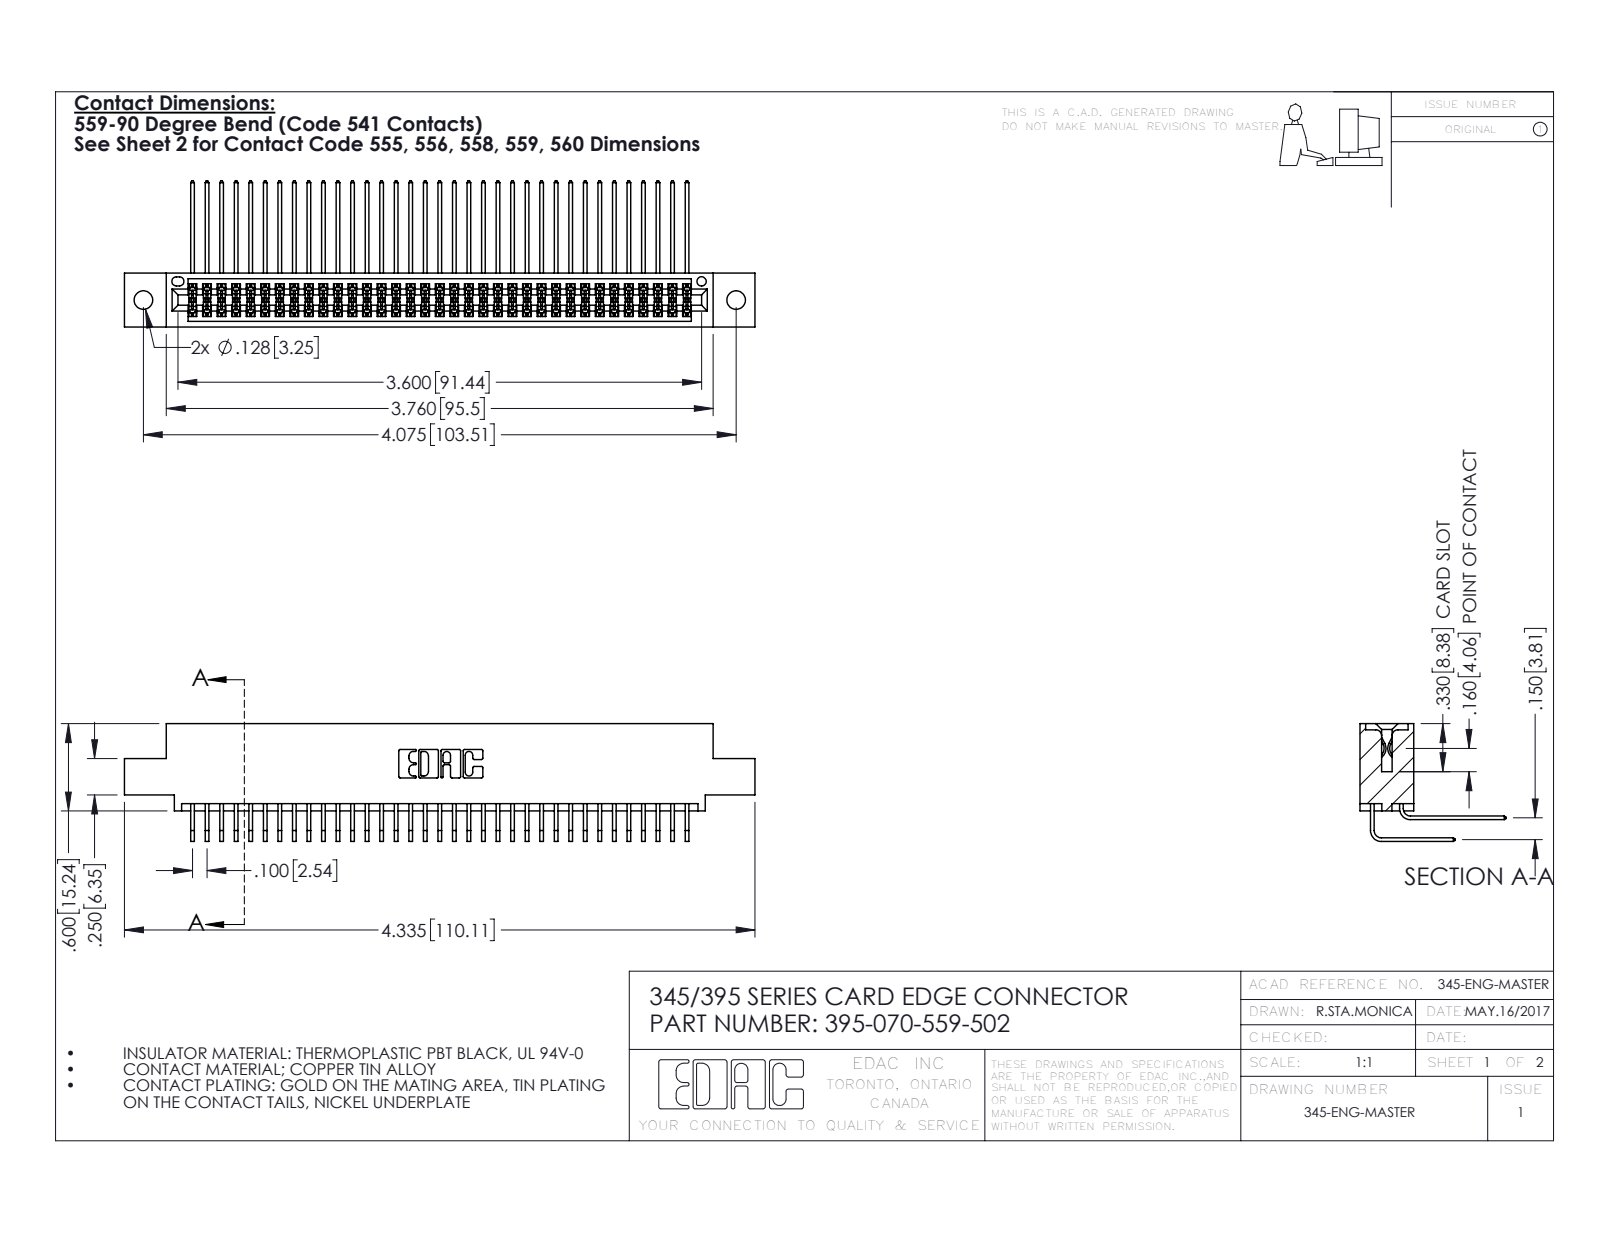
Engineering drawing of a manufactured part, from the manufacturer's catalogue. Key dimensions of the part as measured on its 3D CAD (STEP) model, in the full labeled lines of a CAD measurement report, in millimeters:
Part name (STEP PRODUCT): 345-292-001_558 559 Tail - 1; 345-292-001_559 Tail - 2; 345 Part_0.110 Offset - 0.128 Dia; 395-070-559-502
STEP written by: SolidWorks 2016 (CONFIG_CONTROL_DESIGN)
Units: millimetres
Bodies: 71 solids, 3770 faces (2534 planar, 1236 cylindrical, 0 other)
Overall size (bounding box): 110.1 × 25.5 × 20.5
Volume: 10 900 mm³ · Surface area: 17 730 mm²
Round holes (diameter × count): ⌀3.3 ×2, ⌀1.6 ×1
Partial cylindrical surfaces — rounded edges, fillets, slot ends (radius × count): R0.2 ×105, R0.3 ×22, R0.2 ×6, R0.8 ×6, R0.7 ×3, R0.4 ×2, R0.5 ×2, R0.6 ×2
Main face-to-face distances: 1.8, 7.6, 9.4, 5.1, 2.5, 6.9, 0.6, 5.7, 4.4, 3.8
Hole centre spacings: 6.9, 97.5, 103.5
